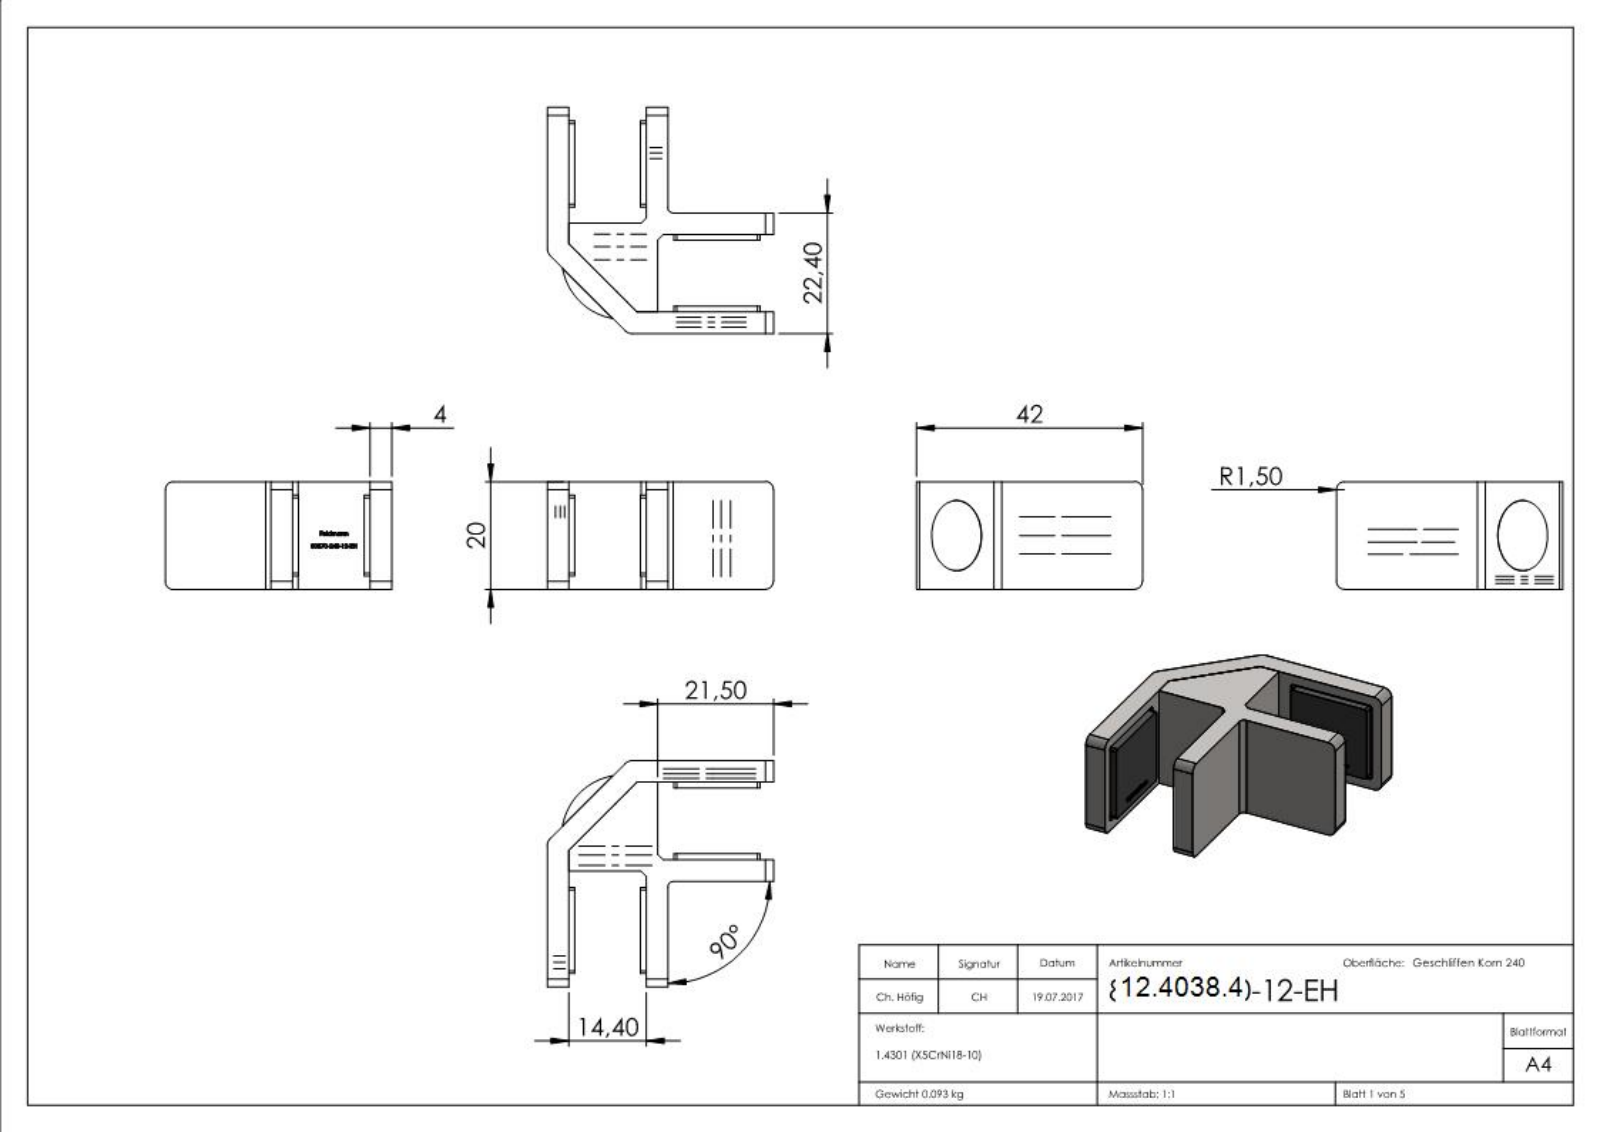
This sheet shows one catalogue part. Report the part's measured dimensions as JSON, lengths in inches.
{"part_name": "80570-xxx-xx-EH Teil3; 80570-xxx-xx-EH Teil1_80570-240-12-EH Teil1; 80570-240-12-EH; 80570-xxx-xx-EH Teil4 (+6 more)", "step_written_by": "SolidWorks 2018 (CONFIG_CONTROL_DESIGN)", "units": "inches", "bodies": {"solids": 8, "faces": 2905, "planar": 1619, "cylindrical": 205, "other": 1081}, "overall_size": [1.654, 1.654, 0.787], "volume_in3": 0.839, "surface_area_in2": 17.31, "round_holes": [[0.106, 2], [0.071, 1], [0.197, 1], [0.276, 1], [0.492, 1]], "round_bosses_or_shafts": [[0.456, 1], [0.236, 1], [0.157, 1]], "partial_cylinders_radius": [[0.008, 56], [0.02, 48], [0.059, 4], [0.079, 2], [0.039, 1]], "face_to_face_distances": [0.138, 0.063, 0.157, 0.744, 0.02, 0.606, 0.724, 0.201, 0.681, 0.543], "hole_center_spacings": [0.323, 0.646]}
